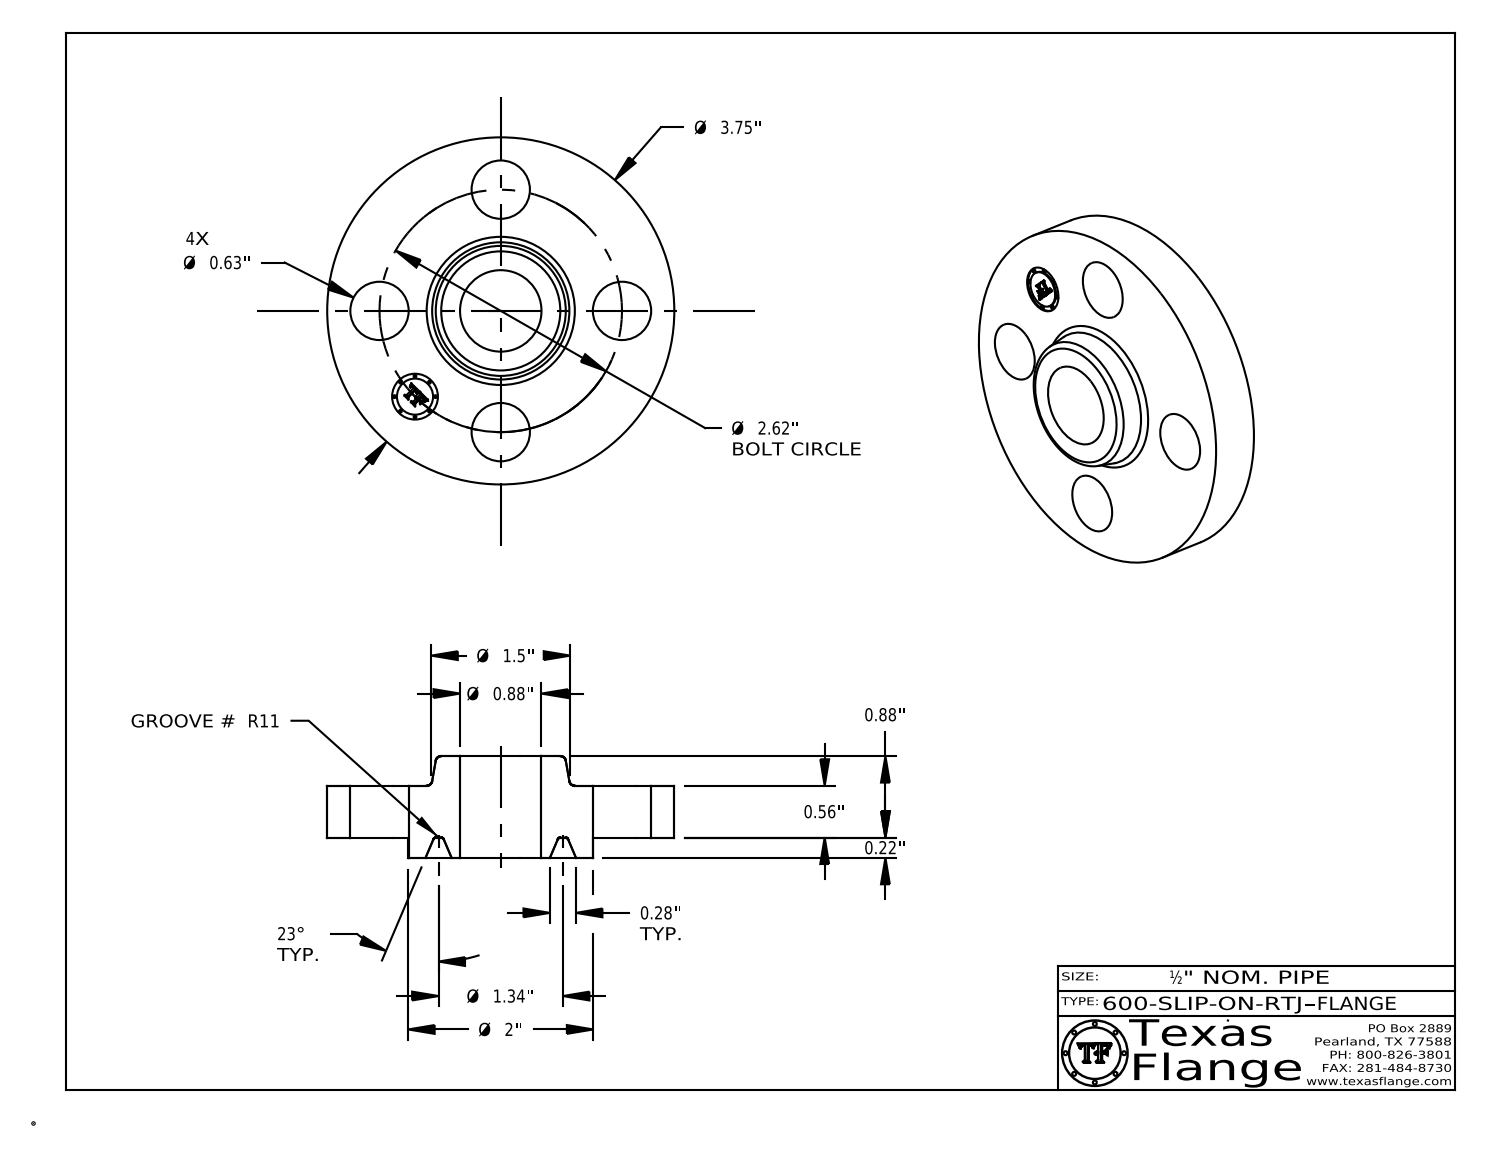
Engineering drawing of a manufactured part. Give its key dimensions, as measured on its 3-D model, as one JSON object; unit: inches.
{"part_name": "600-SLIP-ON-RTJ", "step_written_by": "CATIA V5 STEP AP214 (AUTOMOTIVE_DESIGN)", "units": "inches", "bodies": {"solids": 1, "faces": 423, "planar": 371, "cylindrical": 38, "other": 14}, "overall_size": [3.75, 3.75, 1.099], "volume_in3": 5.855, "surface_area_in2": 36.16, "round_holes": [[0.63, 4], [0.495, 1], [0.88, 1]], "round_bosses_or_shafts": [[0.03, 8], [3.75, 1], [2, 1], [0.39, 1]], "face_to_face_distances": [0.56, 0.219, 0.779, 1.099, 0.88, 0.32, 0.764, 0.545, 0.015, 0.335], "hole_center_spacings": [1.31, 1.852, 1.003, 2.42, 2.62, 1.31]}
